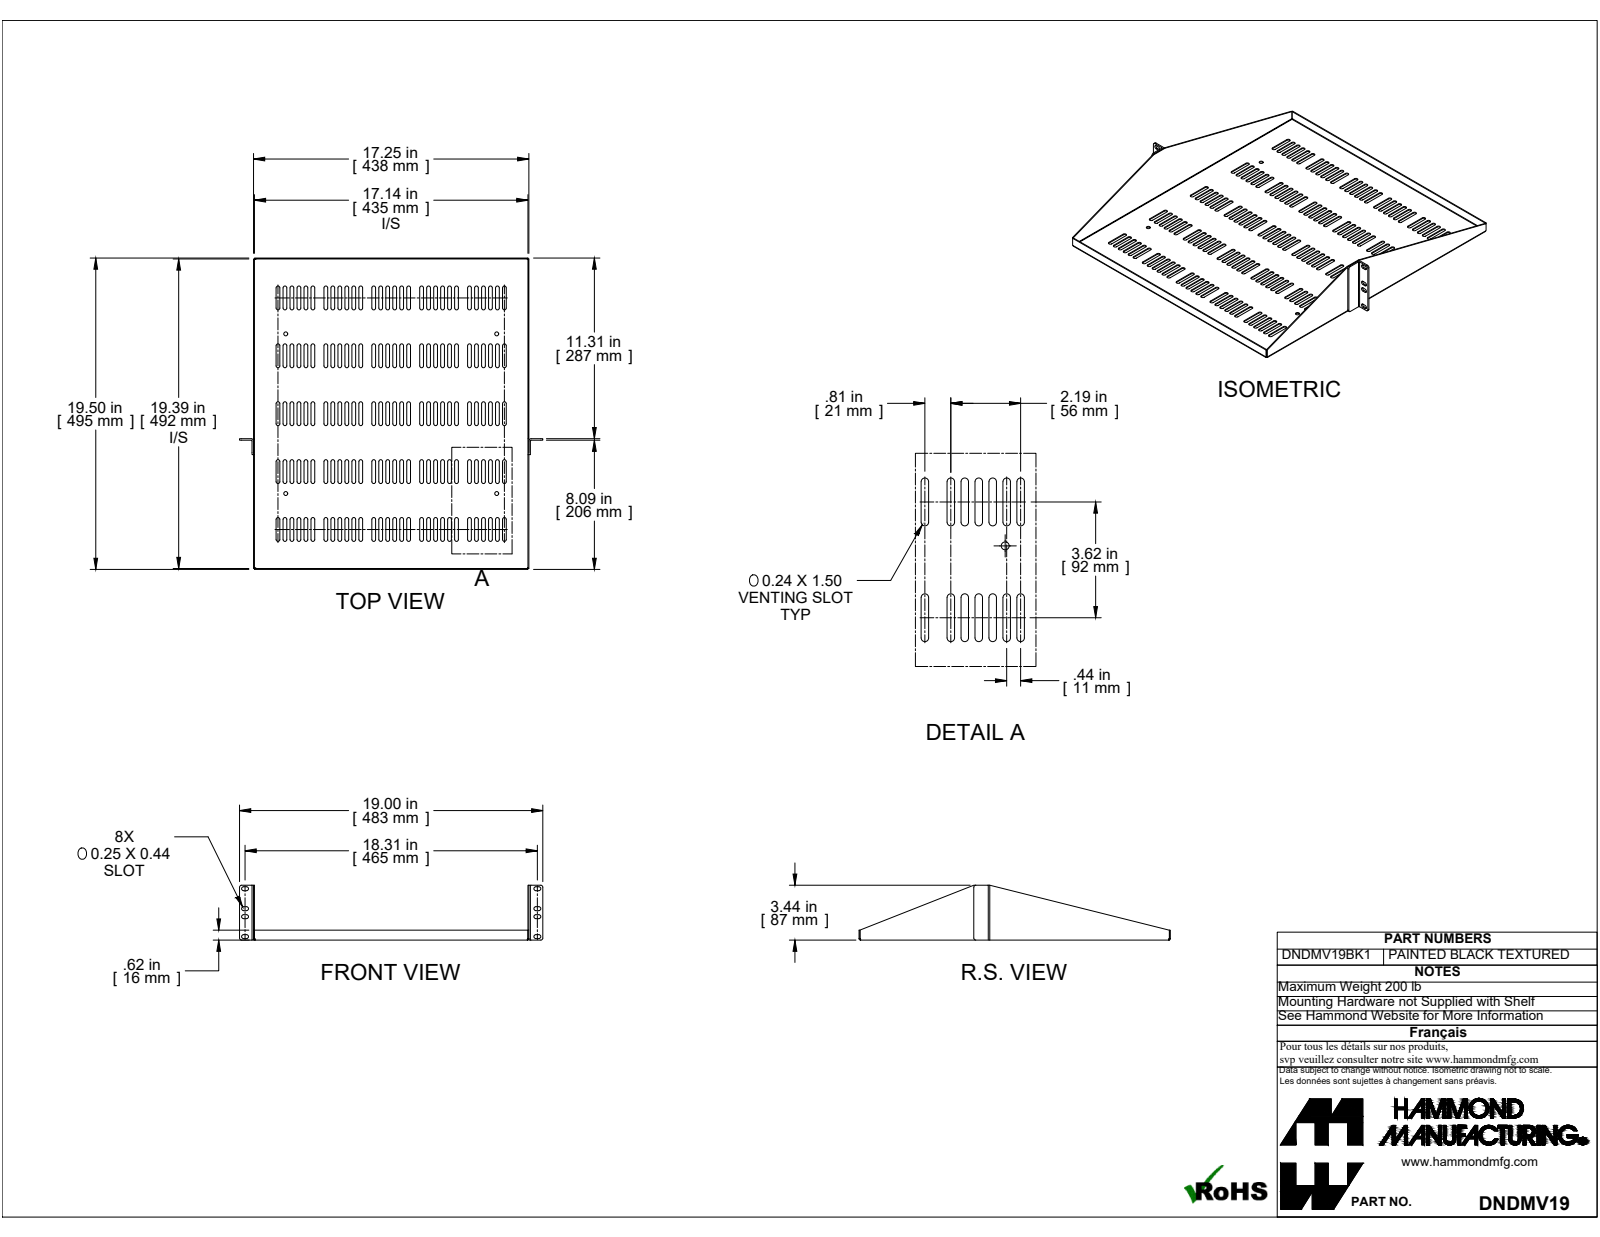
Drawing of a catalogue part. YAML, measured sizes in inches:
part_name: "DNDMV19BK1"
step_written_by: "SolidWorks 2019 (CONFIG_CONTROL_DESIGN)"
units: inches
bodies: {solids: 3, faces: 714, planar: 358, cylindrical: 348, other: 8}
overall_size: [19.5, 19, 3.437]
volume: 22.83
surface_area: 821.8
round_holes:
  - {diameter: 0.25, count: 4}
partial_cylinders:
  - {radius: 0.118, count: 270}
  - {radius: 0.117, count: 30}
  - {radius: 0.125, count: 22}
  - {radius: 0.029, count: 4}
  - {radius: 0.055, count: 4}
  - {radius: 0.086, count: 4}
  - {radius: 0.048, count: 2}
  - {radius: 0.143, count: 2}
face_to_face_distances: [0.057, 0.057, 17.193, 17.25, 17.136, 19.443, 0.095, 19.386, 19.5, 0.152]
hole_center_spacings: [10, 13.218, 16.575]
